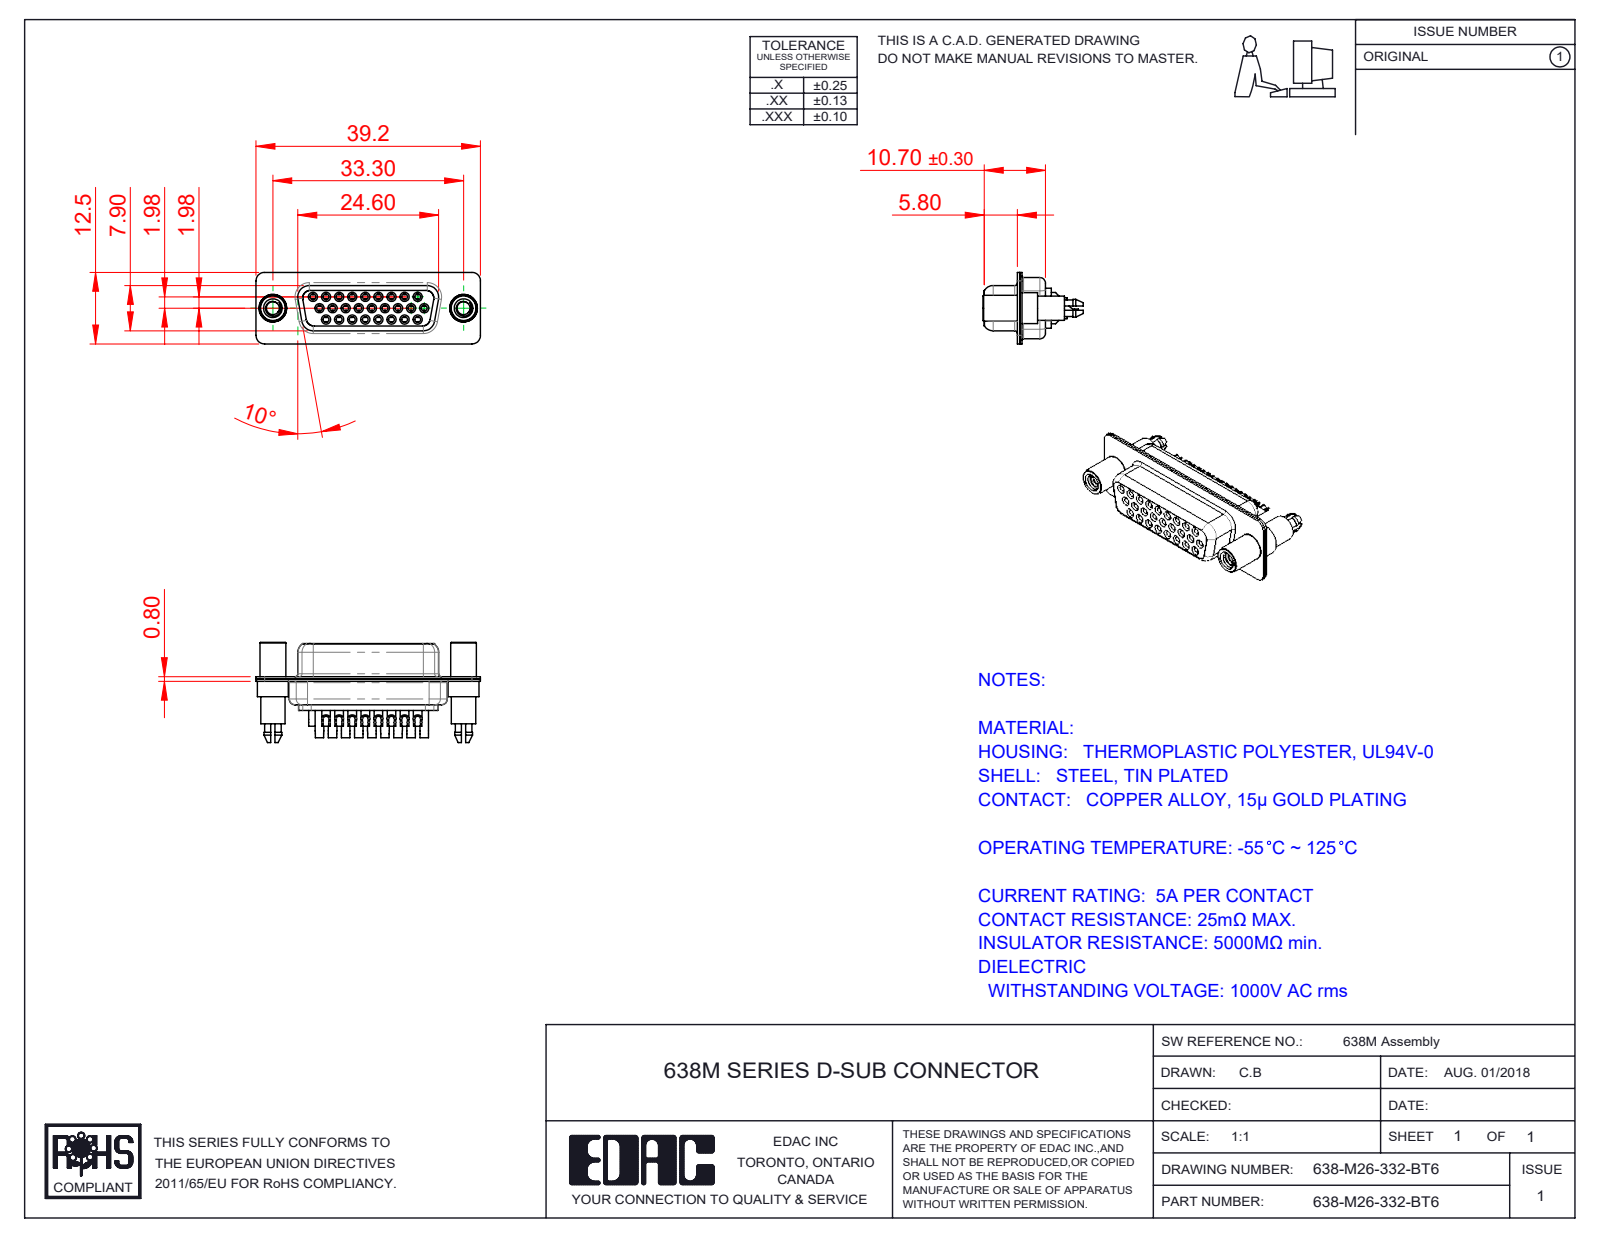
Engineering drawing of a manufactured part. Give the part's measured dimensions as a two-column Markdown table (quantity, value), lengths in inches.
| quantity | value |
| --- | --- |
| part name | 638M Contact Row 2_32; 638-M26-332-BT6; 638M 4-40 Threaded Standoff and Boardlock; 638M Shell Rear_26 Contacts (+4 more) |
| STEP written by | SolidWorks 2020 (CONFIG_CONTROL_DESIGN) |
| units | inches |
| bodies | 31 solids, 1793 faces (547 planar, 719 cylindrical, 527 other) |
| overall size | 1.543 × 0.689 × 0.492 |
| volume | 0.167 in³ |
| surface area | 13.22 in² |
| round holes (diameter × count) | 0.039 × 27, 0.043 × 26, 0.067 × 26, 0.071 × 26, 0.079 × 26, 0.089 × 2, 0.157 × 2, 0.189 × 2 |
| round bosses / shafts (diameter × count) | 0.087 × 26, 0.063 × 26, 0.059 × 26, 0.213 × 2, 0.193 × 2, 0.177 × 2, 0.167 × 2 |
| partial cylindrical surfaces (radius × count) | 0.059 × 18, 0.079 × 12, 0.063 × 10, 0.053 × 8, 0.039 × 7, 0.01 × 4, 0.02 × 4, 0.024 × 4 |
| main face-to-face distances | 0.016, 0.055, 0.018, 0.333, 0.35, 0.039, 0.071, 0.244, 0.278, 0.366 |
| hole center spacings | 0.156, 0.09, 0.18, 0.238, 0.09, 0.324, 0.27, 0.238 |
